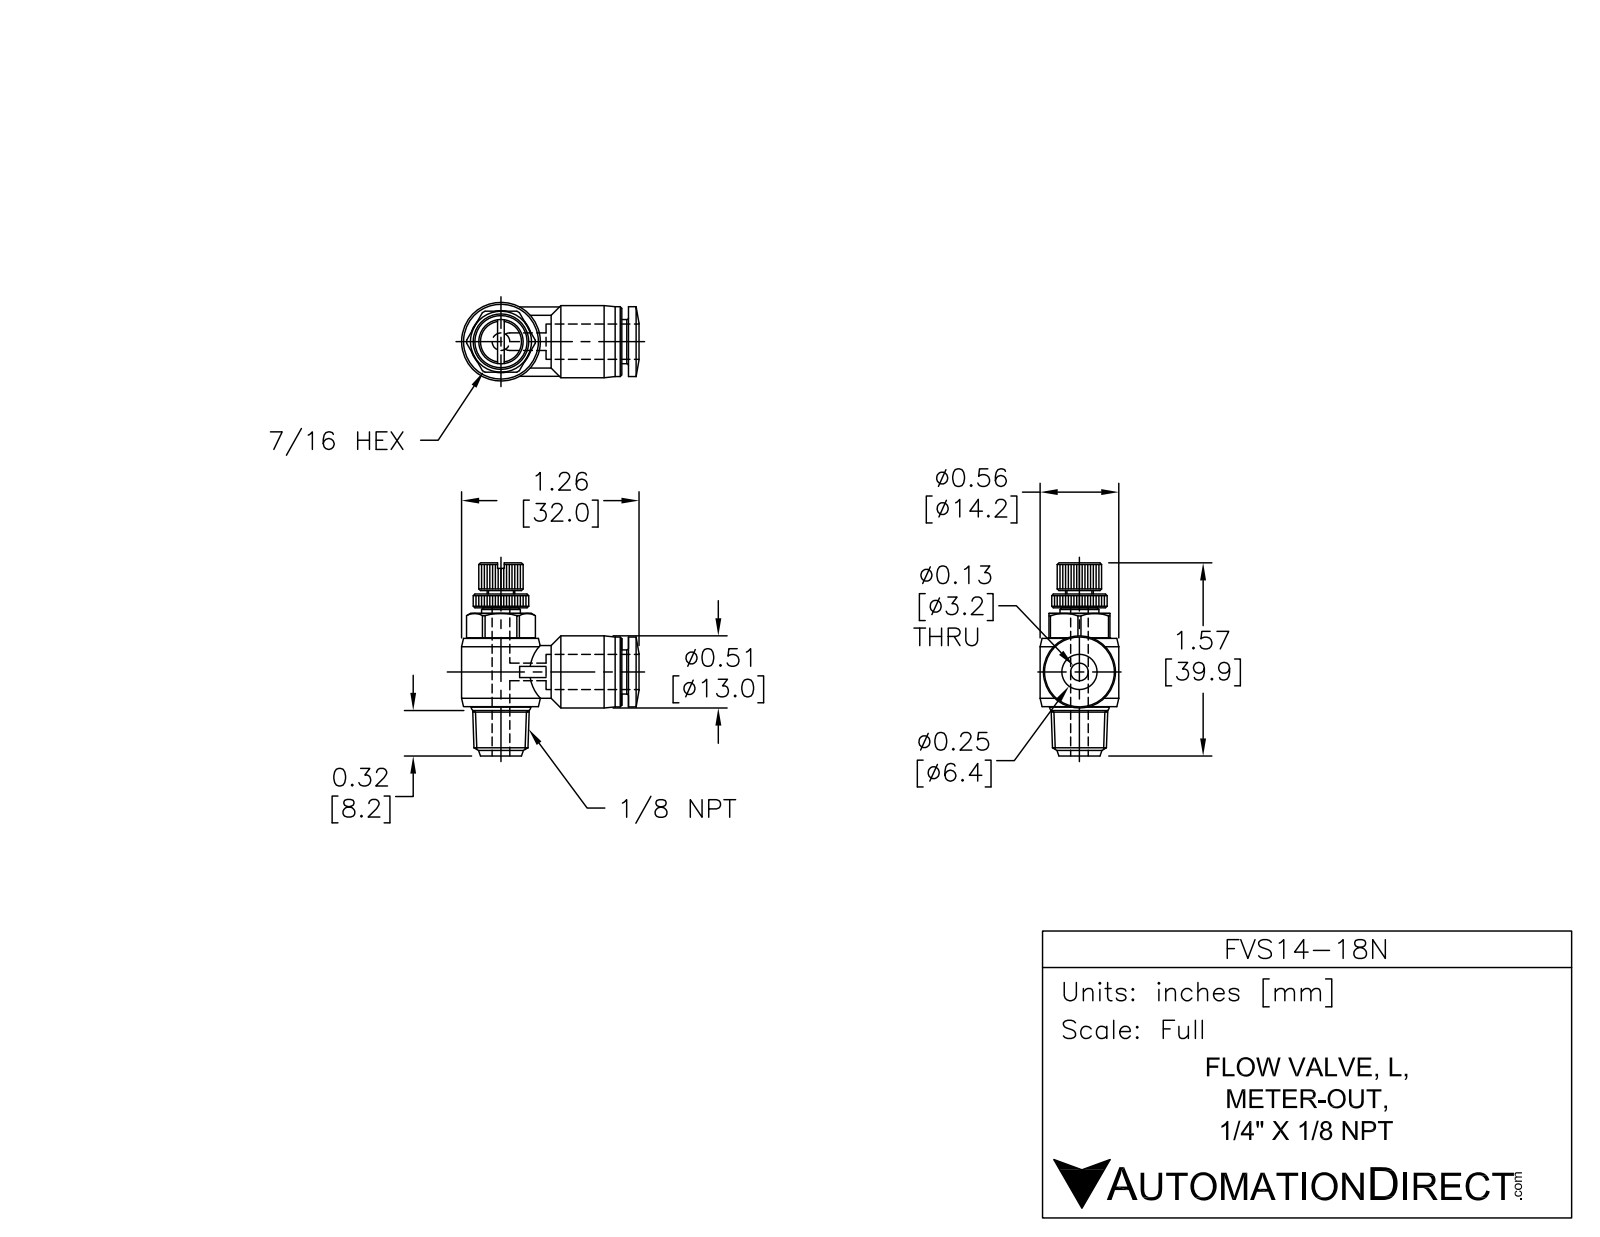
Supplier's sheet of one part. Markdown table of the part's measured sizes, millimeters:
| quantity | value |
| --- | --- |
| part name | FVS14-18N |
| STEP written by | SolidWorks 2015 (AUTOMOTIVE_DESIGN) |
| units | millimeters |
| bodies | 1 solid, 507 faces (198 planar, 113 cylindrical, 196 other) |
| overall size | 39.8 × 32 × 14.2 |
| volume | 4 980 mm³ |
| surface area | 3 251 mm² |
| round holes (diameter × count) | 3 × 2, 6.6 × 1 |
| round bosses / shafts (diameter × count) | 14.2 × 1, 13 × 1, 12.6 × 1, 11.2 × 1, 10.3 × 1, 9.5 × 1, 8 × 1, 7 × 1 |
| partial cylindrical surfaces (radius × count) | 4 × 1, 5 × 1, 6.2 × 1 |
| main face-to-face distances | 11, 1.2, 16.8, 5.2, 20.3, 3.5, 1, 12.3, 4.5, 8 |
